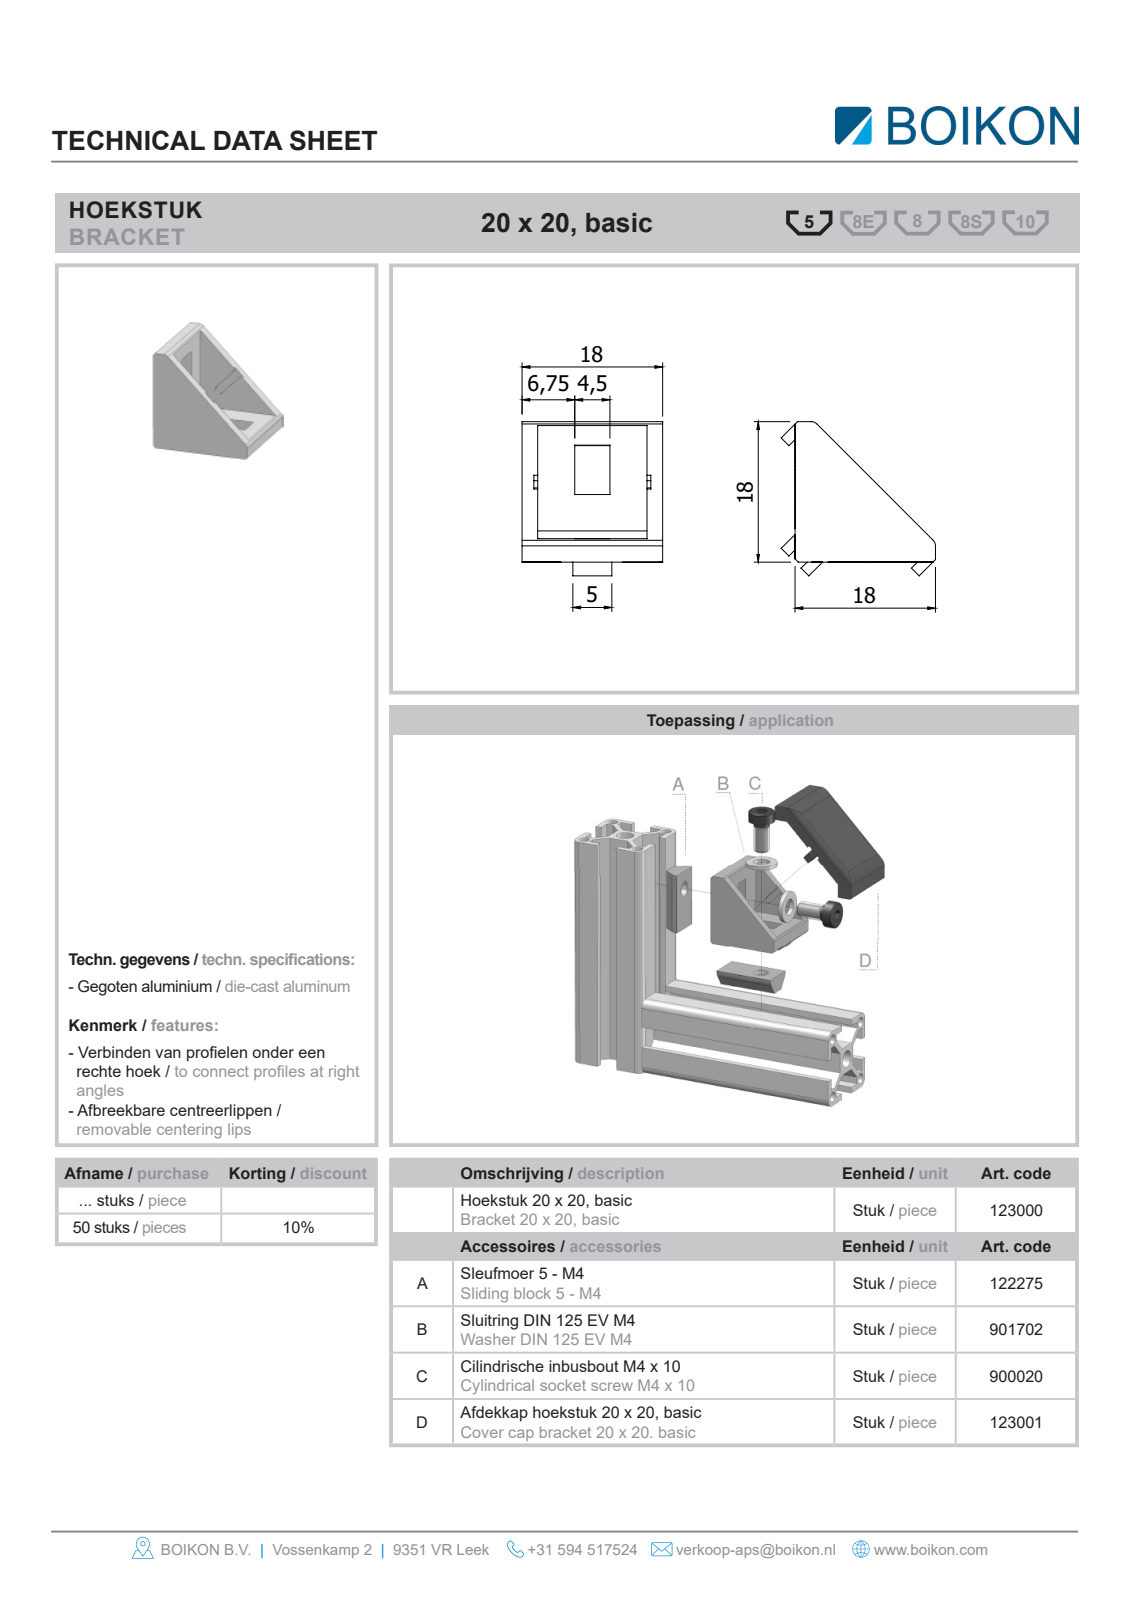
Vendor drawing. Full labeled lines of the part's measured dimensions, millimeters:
Part name (STEP PRODUCT): Root; 123000HOEKSTUK 20X20 BASICBOIKON; 123001AFDEKKAP HOEKSTUK 20X20 BASICBOIKON; 122280Sleufmoer 5 - M5 met kogelBOIKON (+2 more)
STEP written by: HiCAD 2013 1802.4 Build 509 (AUTOMOTIVE_DESIGN)
Units: millimetres
Bodies: 8 solids, 215 faces (156 planar, 51 cylindrical, 8 other)
Overall size (bounding box): 27.46 × 27.46 × 18
Volume: 4 191 mm³ · Surface area: 5 345 mm²
Round holes (diameter × count): ⌀2.96 ×2, ⌀5 ×2, ⌀5.3 ×2
Round bosses / shafts (diameter × count): ⌀10 ×2, ⌀4.02 ×2
Partial cylindrical surfaces — rounded edges, fillets, slot ends (radius × count): R0.4 ×4, R0.7 ×4, R8.5 ×4, R1 ×3, R0.5 ×2, R1.5 ×2, R2 ×2, R4 ×2
Main face-to-face distances: 2, 3, 1.8, 15.8, 4.8, 1, 18, 1.5, 4, 17.8
Hole centre spacings: 6
